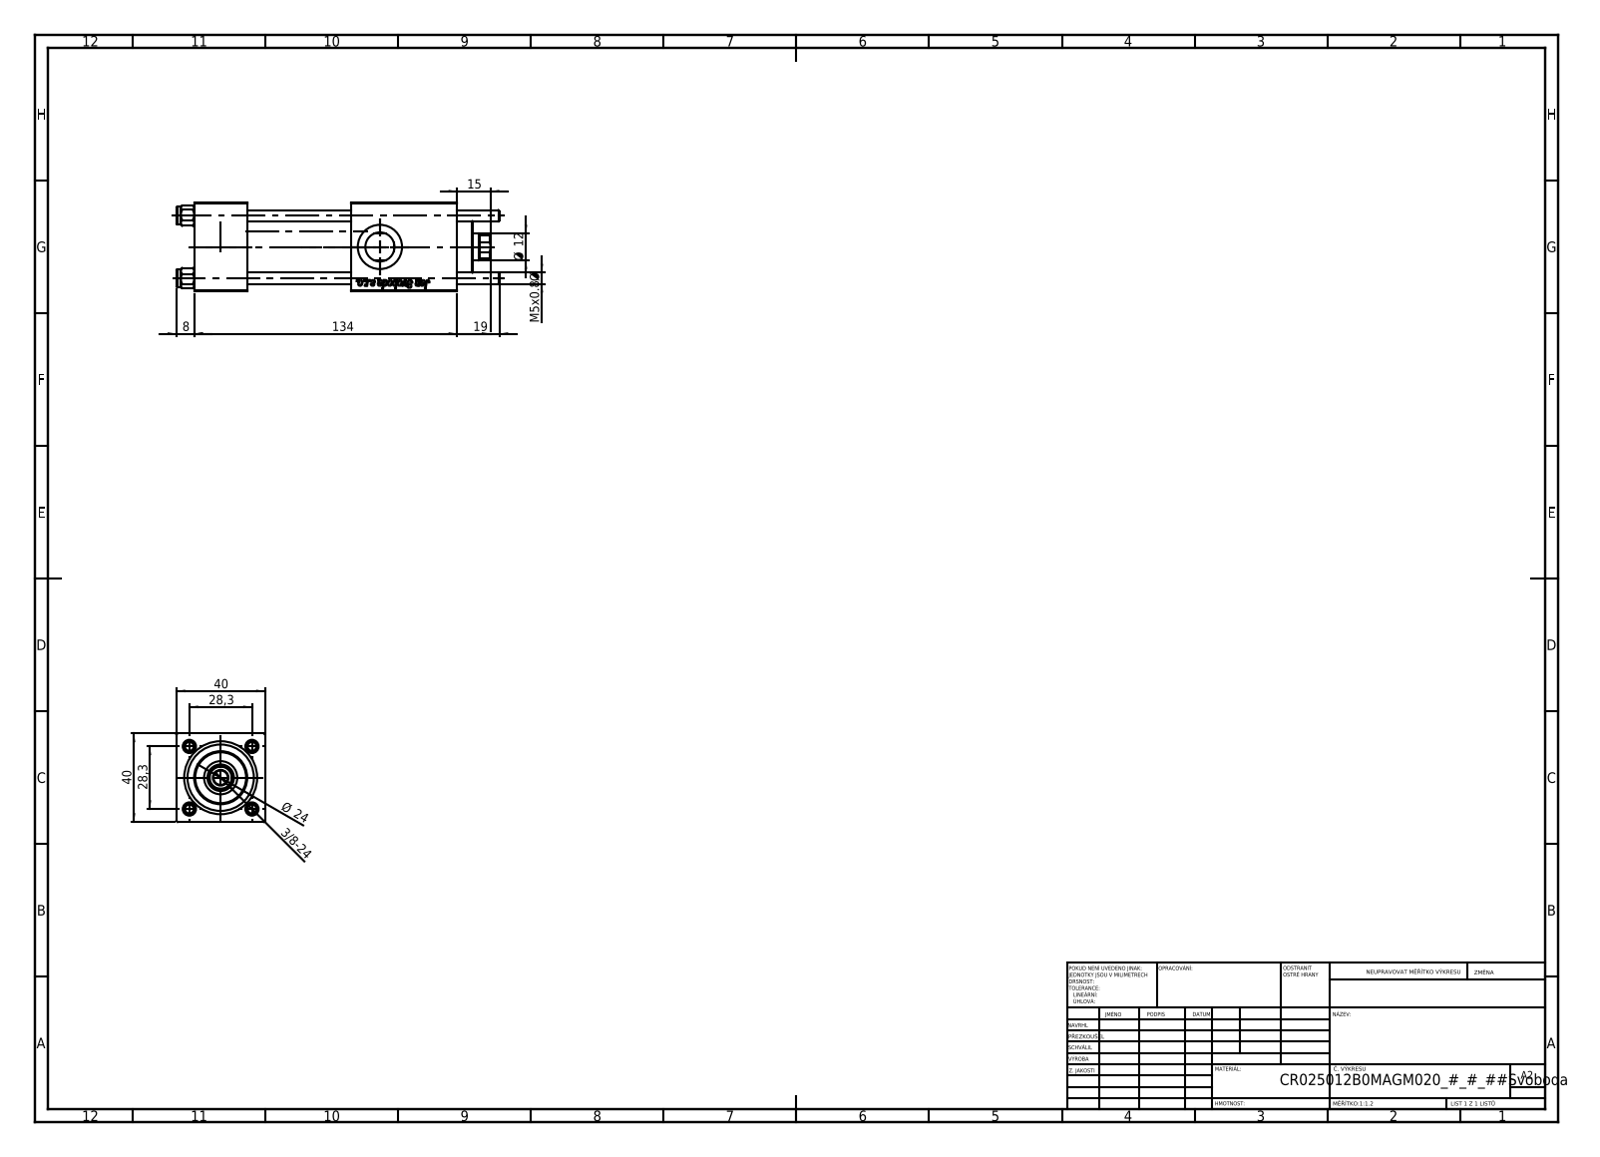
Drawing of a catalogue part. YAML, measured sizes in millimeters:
part_name: "V215CR_B-1; V215CR_B_TYCINKA; V215CR_VCP_B; V215_VC_A (+1 more)"
step_written_by: "SolidWorks 2019 (CONFIG_CONTROL_DESIGN)"
units: millimeters
bodies: {solids: 11, faces: 1156, planar: 429, cylindrical: 79, other: 648}
overall_size: [146, 40, 40]
volume: 144840
surface_area: 58622
round_holes:
  - {diameter: 5, count: 4}
  - {diameter: 7, count: 2}
  - {diameter: 13.16, count: 2}
  - {diameter: 20, count: 2}
  - {diameter: 6.5, count: 1}
  - {diameter: 12, count: 1}
  - {diameter: 13, count: 1}
  - {diameter: 15, count: 1}
  - {diameter: 25, count: 1}
  - {diameter: 30, count: 1}
round_bosses_or_shafts:
  - {diameter: 8, count: 4}
  - {diameter: 31, count: 1}
  - {diameter: 24, count: 1}
partial_cylinders:
  - {radius: 5.5, count: 1}
face_to_face_distances: [40, 24, 90.3, 66.3, 71, 47, 19.3, 119, 95, 48]
hole_center_spacings: [20.01, 28.3, 40.02]
